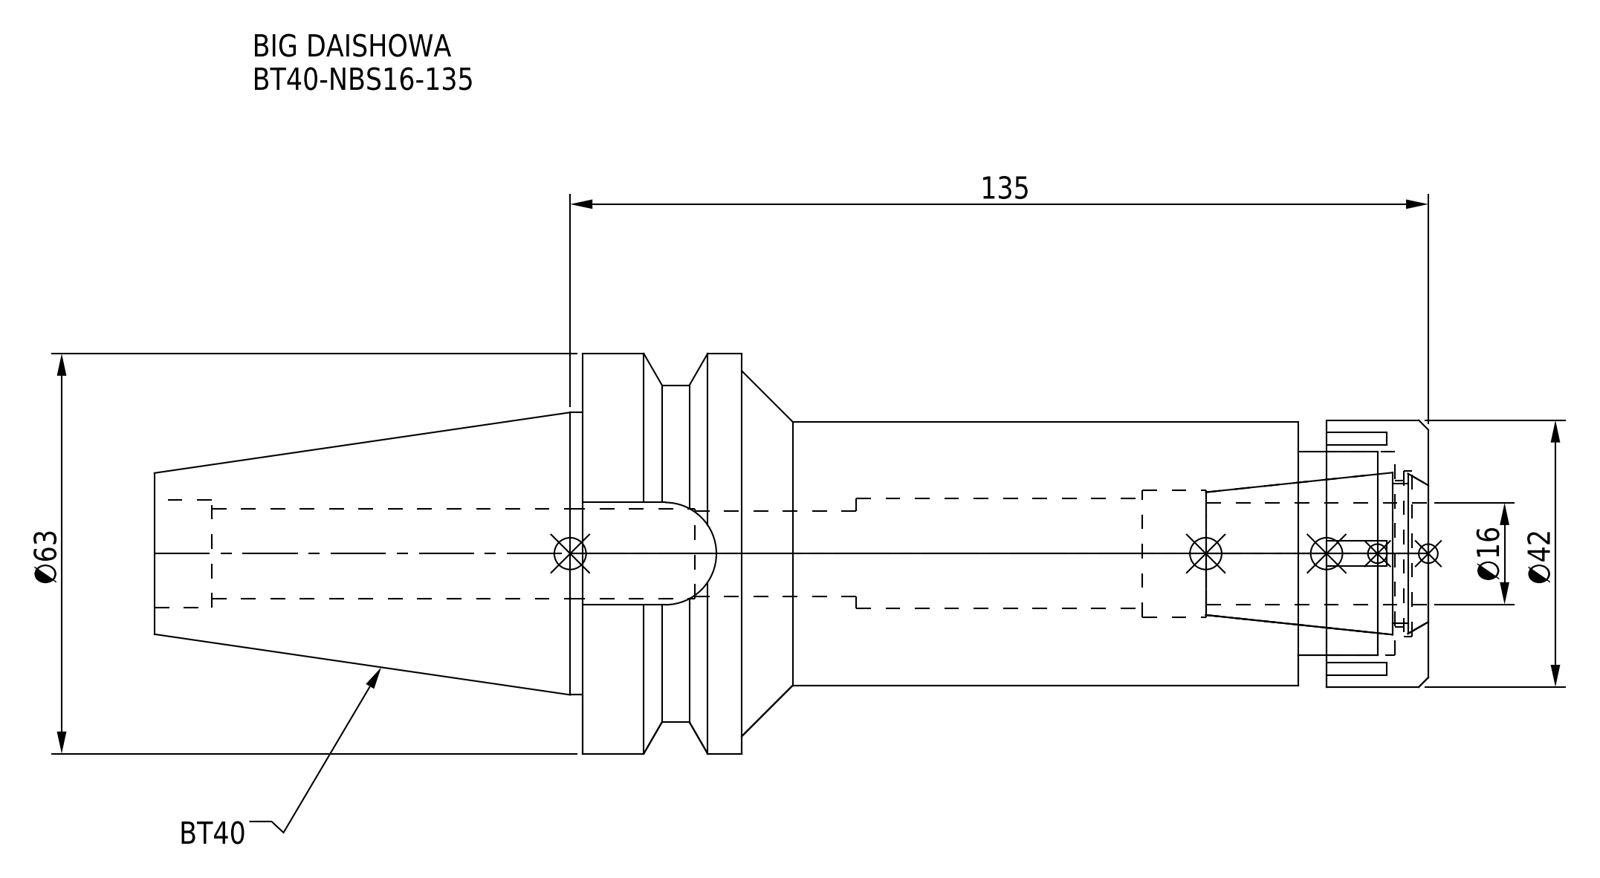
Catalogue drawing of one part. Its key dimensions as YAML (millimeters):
part_name: "DXF_TEMP_ASSY_ASM_4_ASM.stp; BT40-NBS16-135; BT40-NBS16-135-FreeParts; NBN16_1.stp (+3 more)"
step_written_by: "SolidWorks 2019 (CONFIG_CONTROL_DESIGN)"
units: millimeters
bodies: {solids: 2, faces: 93, planar: 45, cylindrical: 34, other: 14}
overall_size: [200.4, 63, 63]
volume: 235978
surface_area: 46265
round_holes:
  - {diameter: 13.5, count: 1}
  - {diameter: 14.2, count: 1}
  - {diameter: 17, count: 1}
  - {diameter: 17.3, count: 1}
  - {diameter: 20, count: 1}
  - {diameter: 23, count: 1}
  - {diameter: 26, count: 1}
  - {diameter: 32, count: 1}
round_bosses_or_shafts:
  - {diameter: 63, count: 1}
  - {diameter: 53, count: 1}
  - {diameter: 44.45, count: 1}
  - {diameter: 42, count: 1}
  - {diameter: 41.5, count: 1}
partial_cylinders:
  - {radius: 8.05, count: 1}
face_to_face_distances: [133, 8, 20.5, 112.5, 16, 4.5, 117, 108, 92, 87.5]
